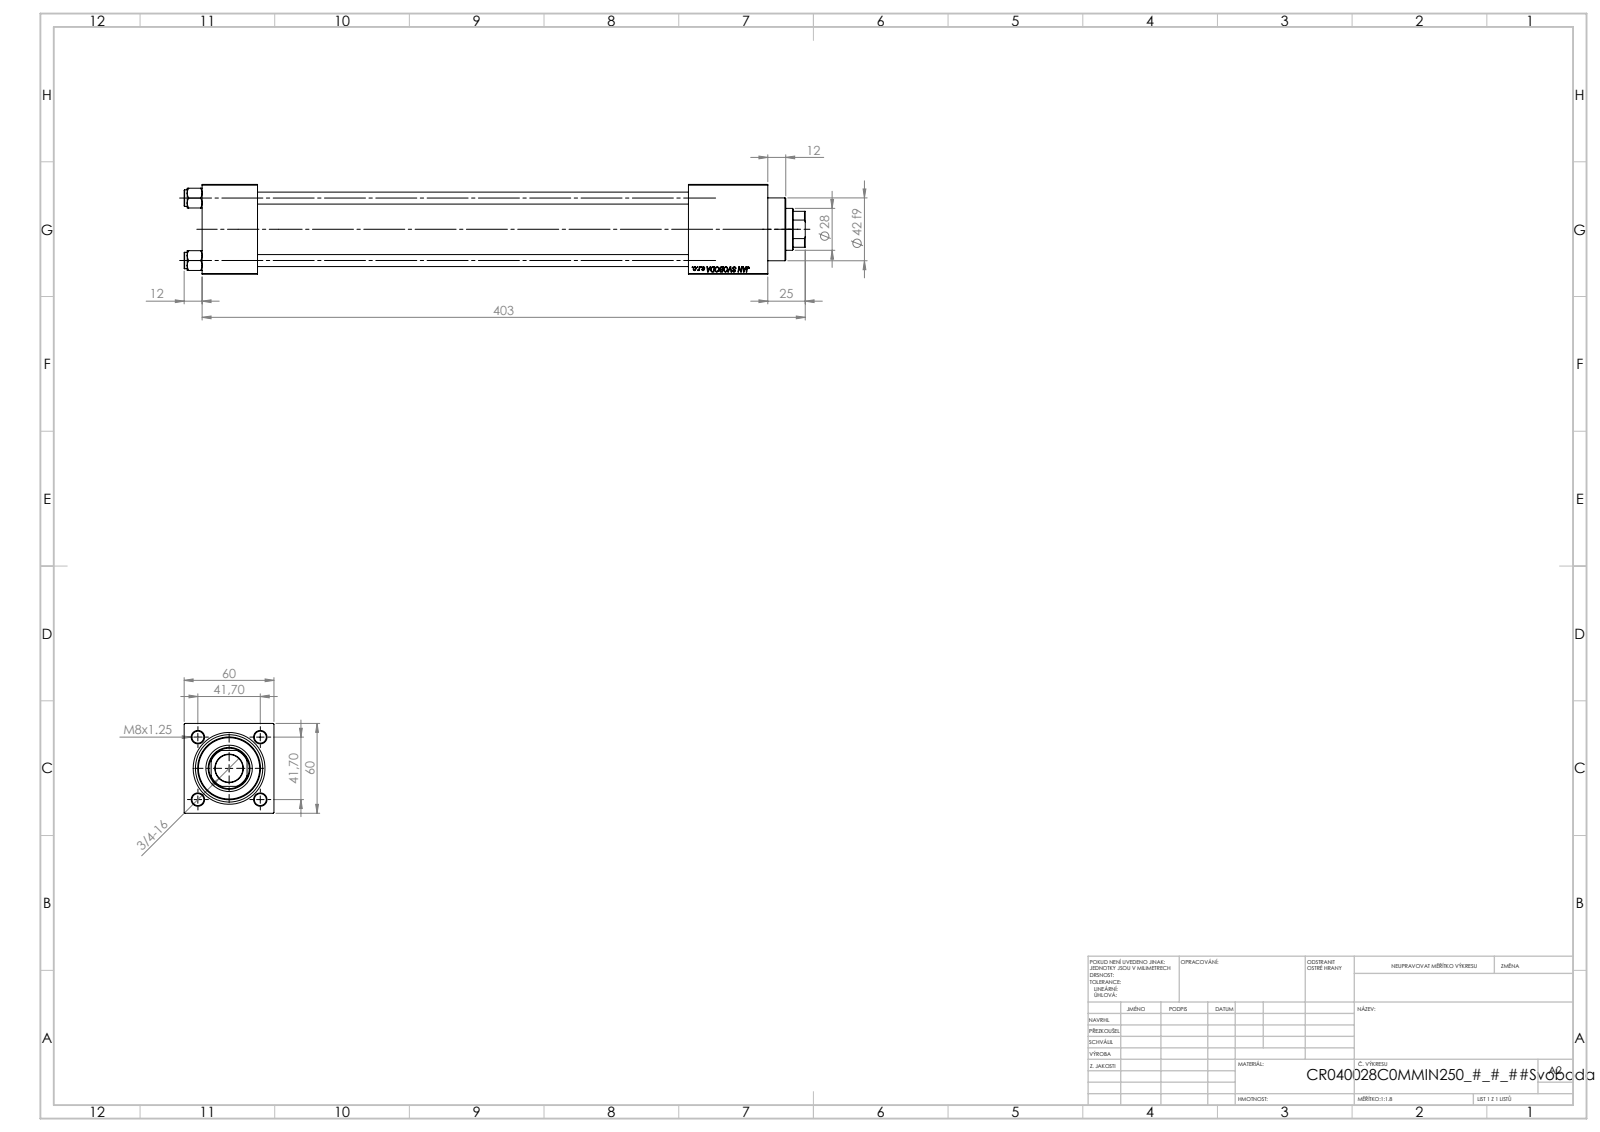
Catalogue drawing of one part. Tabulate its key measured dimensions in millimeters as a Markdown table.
| quantity | value |
| --- | --- |
| part name | V215CR_C_TYCINKA; V215CR_VCP_C; V215_VC_A; V215CR_C_Body (+1 more) |
| STEP written by | SolidWorks 2019 (CONFIG_CONTROL_DESIGN) |
| units | millimeters |
| bodies | 11 solids, 1148 faces (526 planar, 86 cylindrical, 536 other) |
| overall size | 415 × 60 × 60 |
| volume | 705 567 mm³ |
| surface area | 216 841 mm² |
| round holes (diameter × count) | 8 × 4, 7 × 2, 16.66 × 2, 24 × 2, 18.5 × 1, 28 × 1, 31 × 1, 40 × 1, 45 × 1 |
| round bosses / shafts (diameter × count) | 11 × 4, 46 × 1, 42 × 1 |
| partial cylindrical surfaces (radius × count) | 13.5 × 1 |
| main face-to-face distances | 60, 37, 325, 288, 349.3, 312.3, 24.3, 53, 378, 341 |
| hole center spacings | 29.49, 41.7, 58.97, 322.5 |
